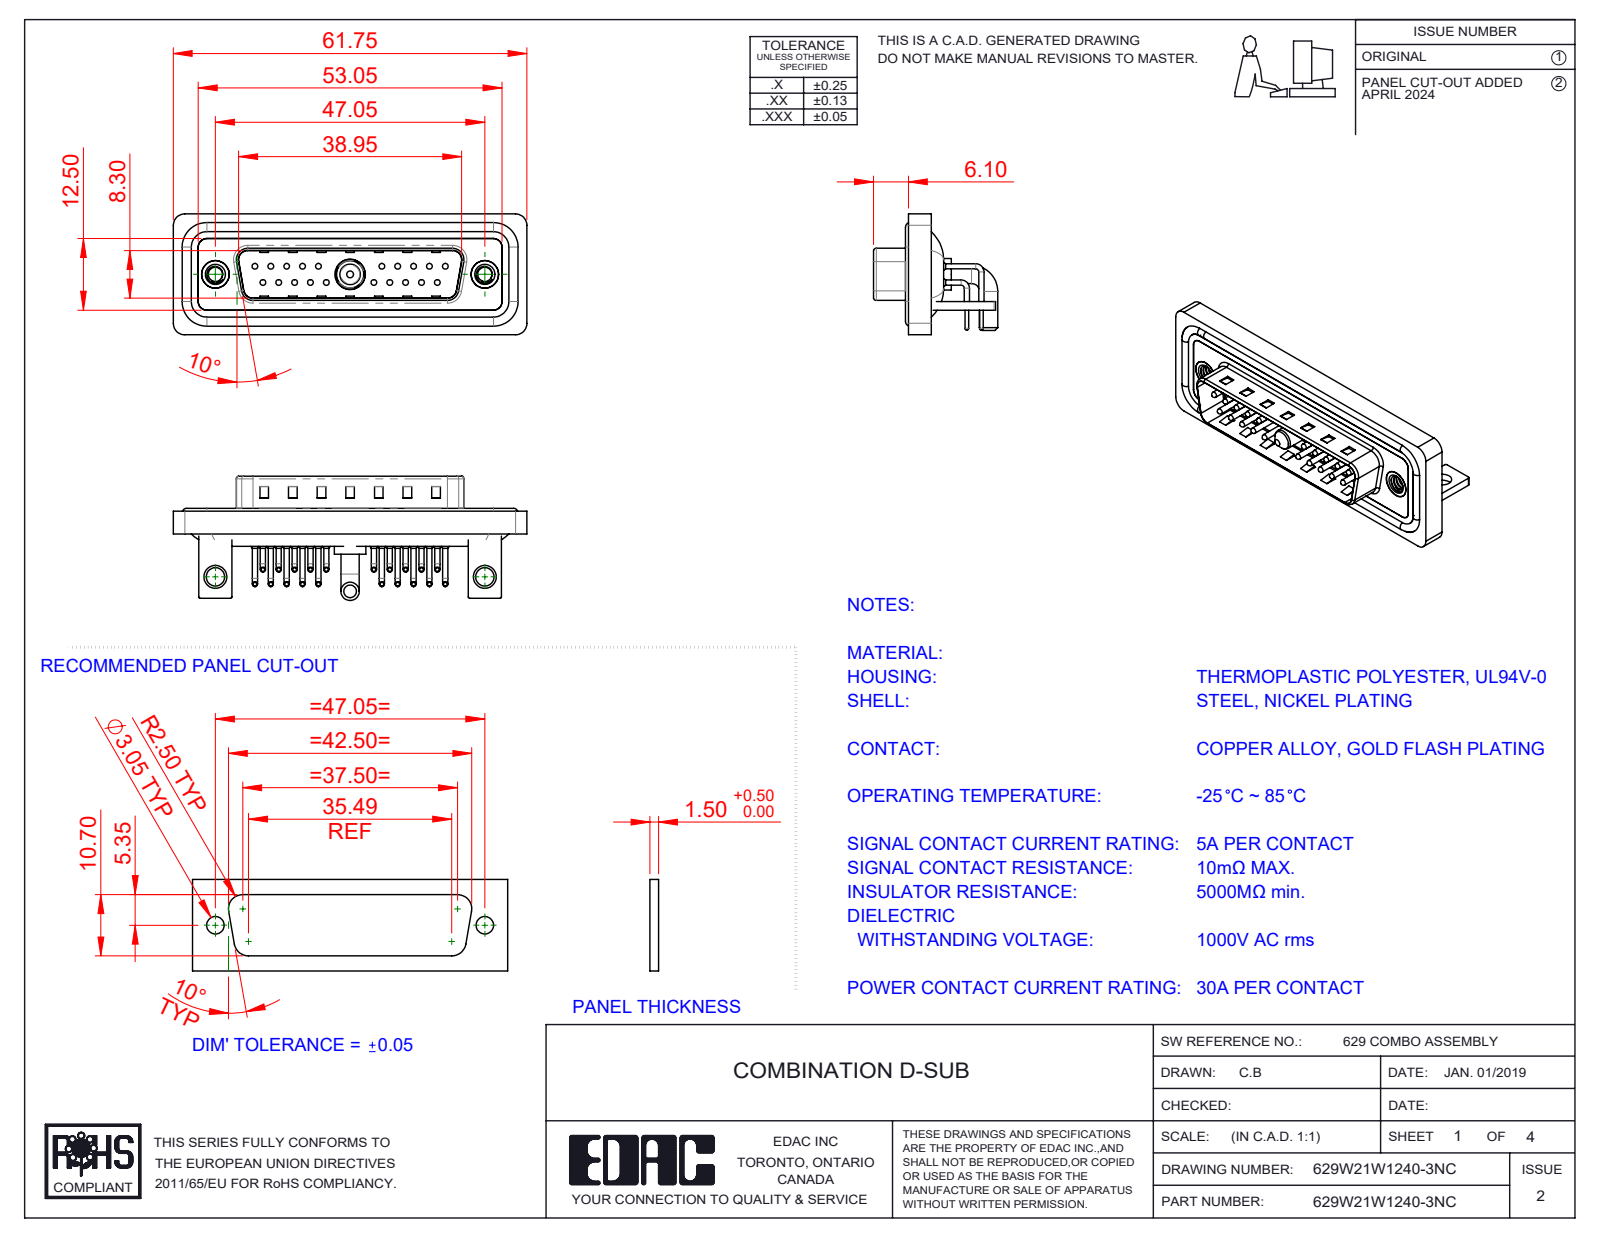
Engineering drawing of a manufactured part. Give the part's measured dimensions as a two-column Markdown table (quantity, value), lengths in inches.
| quantity | value |
| --- | --- |
| part name | 629Combo Contact Row 1; 629Combo Shell Front_25 Contacts; 629Combo Contact Row 2; 629Combo Housing_21W1 (+6 more) |
| STEP written by | SolidWorks 2023 (CONFIG_CONTROL_DESIGN) |
| units | inches |
| bodies | 31 solids, 2764 faces (1519 planar, 947 cylindrical, 298 other) |
| overall size | 2.431 × 0.854 × 0.831 |
| volume | 0.471 in³ |
| surface area | 20.66 in² |
| round holes (diameter × count) | 0.03 × 20, 0.063 × 20, 0.079 × 20, 0.098 × 2, 0.126 × 2, 0.157 × 2, 0.189 × 2, 0.197 × 2, 0.191 × 1, 0.209 × 1 |
| round bosses / shafts (diameter × count) | 0.035 × 40, 0.059 × 20, 0.039 × 20, 0.026 × 20, 0.063 × 4, 0.193 × 2, 0.126 × 2, 0.217 × 1 |
| partial cylindrical surfaces (radius × count) | 0.04 × 20, 0.079 × 19, 0.059 × 18, 0.01 × 16, 0.02 × 9, 0.063 × 8, 0.024 × 4, 0.026 × 4 |
| main face-to-face distances | 0.016, 0.031, 0.083, 0.114, 0.059, 0.043, 0.161, 0.063, 0.177, 0.146 |
| hole center spacings | 0.124, 0.109, 0.218, 0.327, 0.198, 0.763, 0.826, 0.872 |
